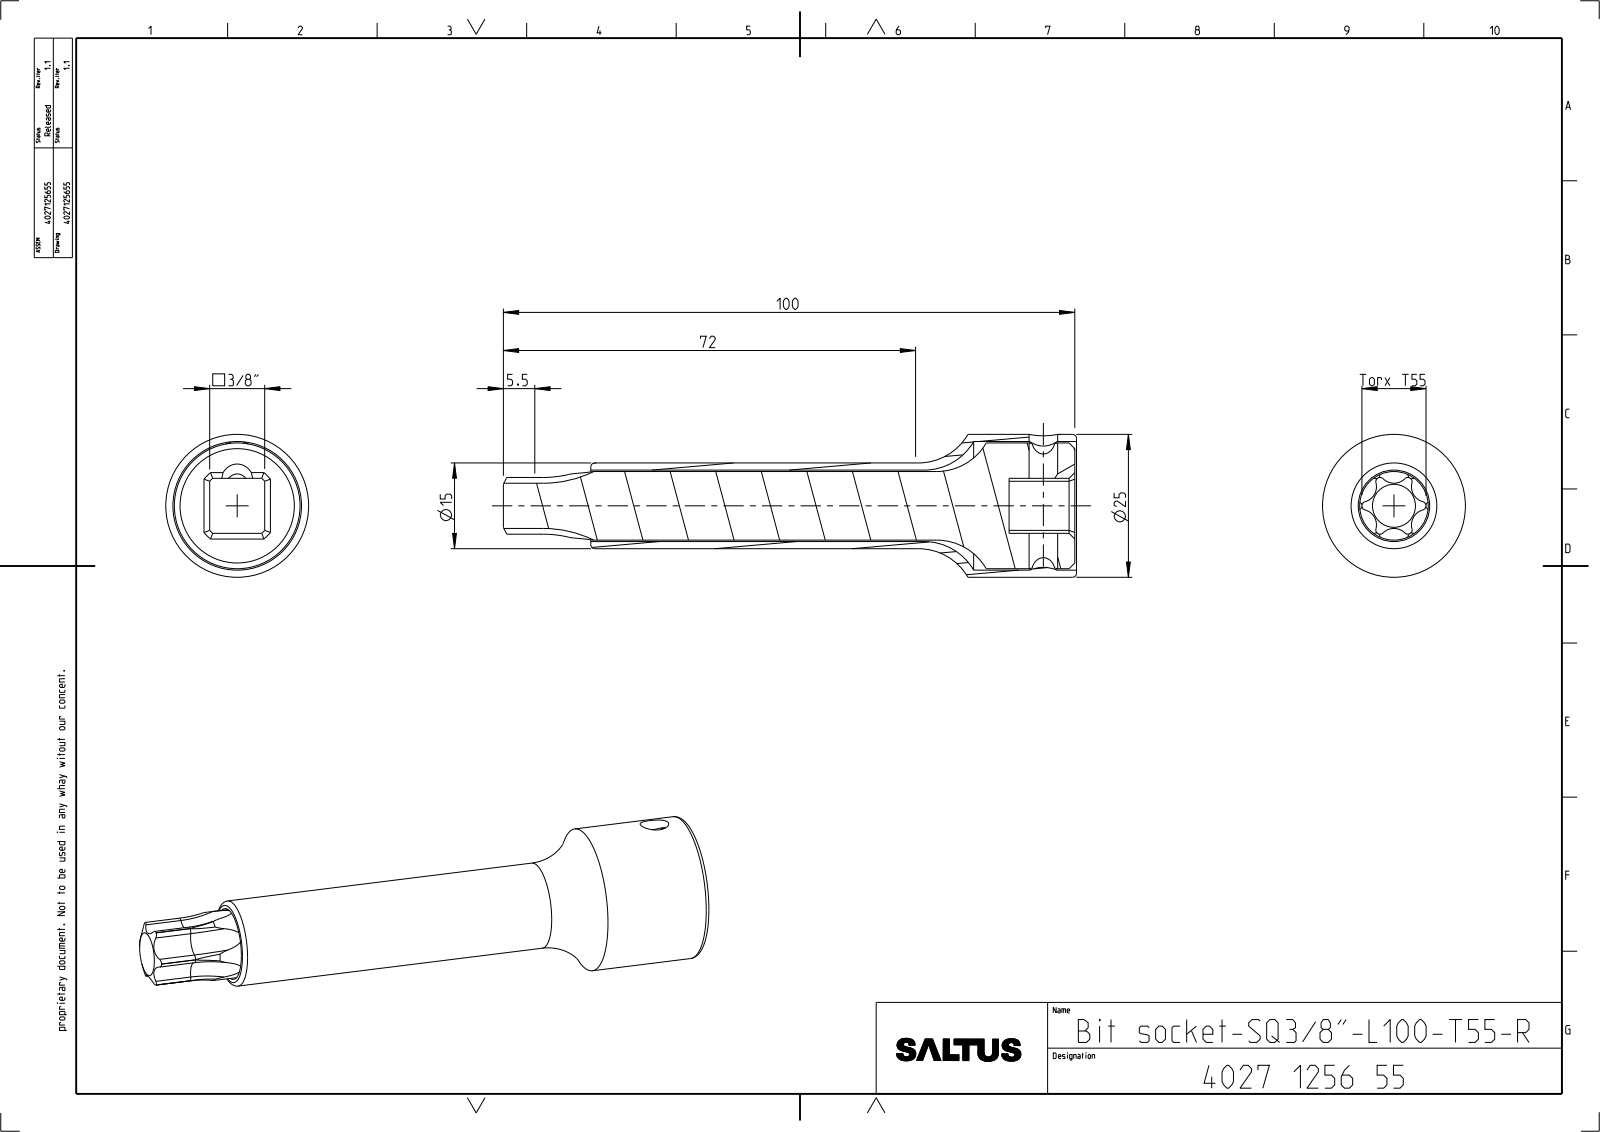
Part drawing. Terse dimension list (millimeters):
name: 4027122755; 4027041661; 4027125655_ASM
written by: CREO PARAMETRIC BY PTC INC, 2022414 (CONFIG_CONTROL_DESIGN)
unit: mm
bodies: 2 solids, 110 faces (14 planar, 51 cylindrical, 45 other)
size: 100.3 × 25 × 25
volume: 19 617 mm³; area: 14 381 mm²
holes: 1× ⌀5, 1× ⌀12.5, 1× ⌀22.5
bosses: 1× ⌀25, 1× ⌀22, 1× ⌀15, 1× ⌀12
rounds: 12× R0.73, 6× R2.71, 1× R3, 1× R5.61, 1× R6.45
face distances: 9.62, 11.5, 100, 88.5, 11.8, 100.3, 85, 84.7, 73.2, 15.3
